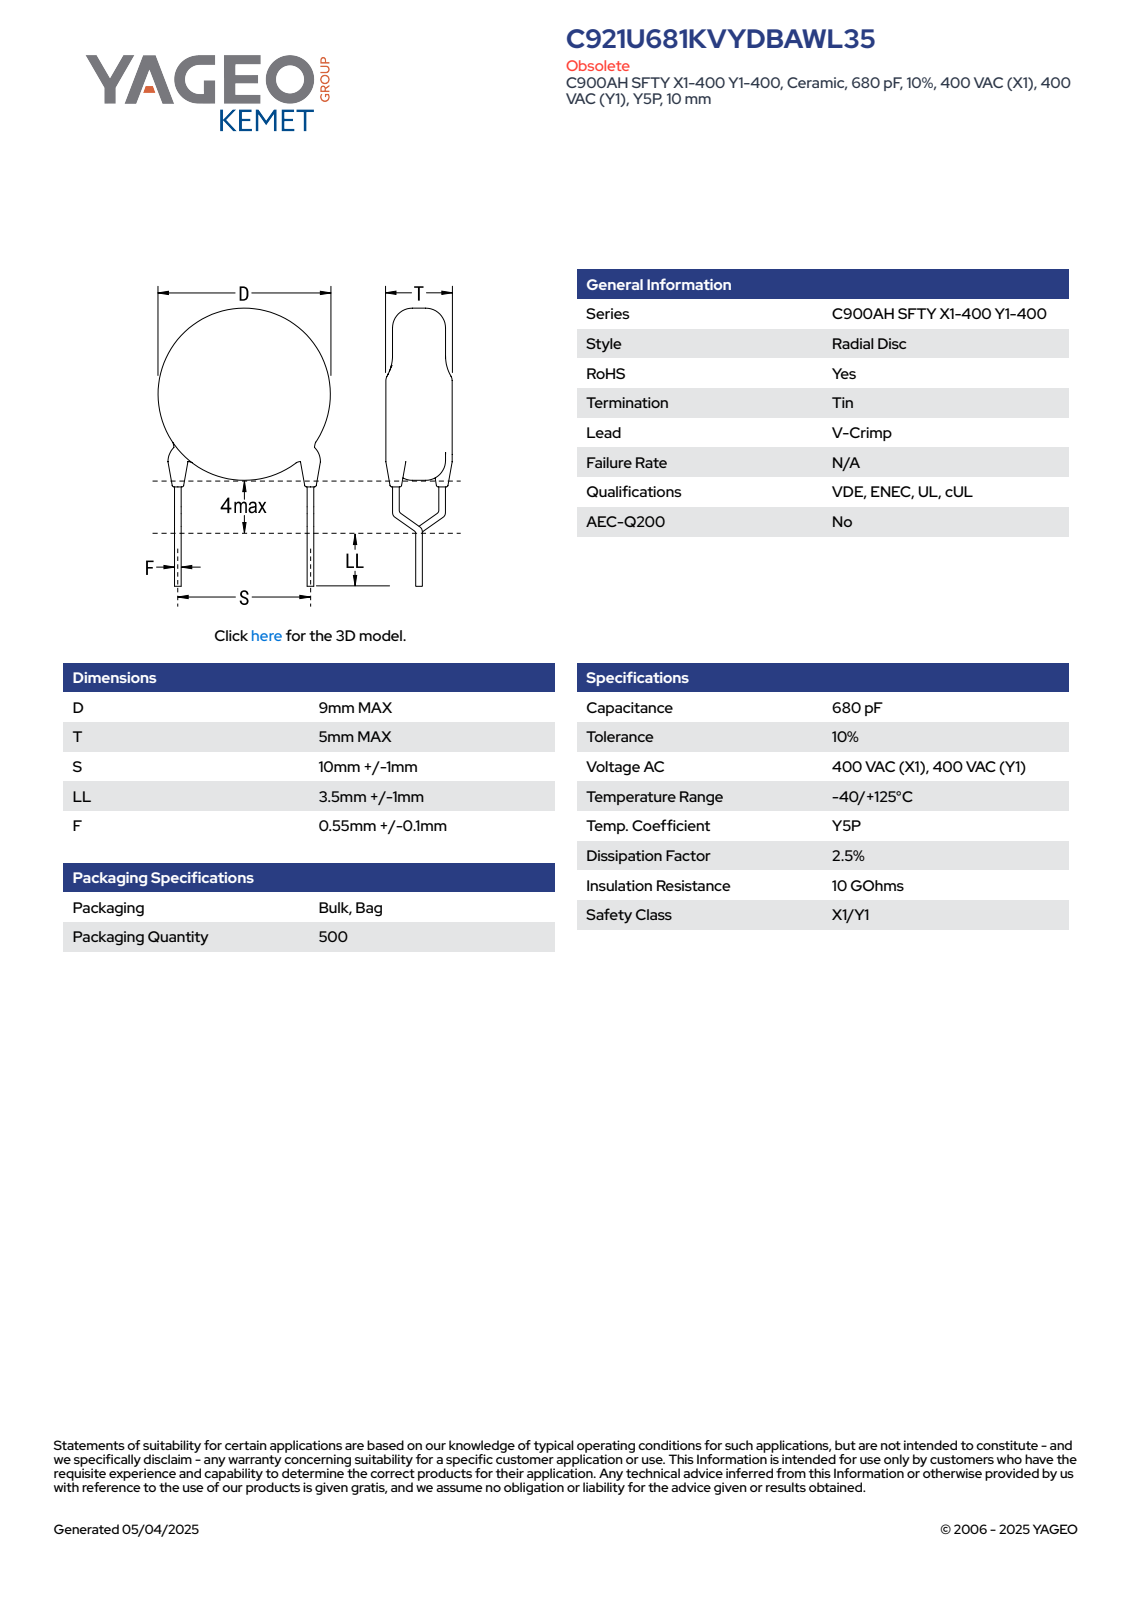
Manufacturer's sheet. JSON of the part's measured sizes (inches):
{"part_name": "CCD_VCC900_D9T5S10LL4.5F0.65", "step_written_by": "SolidWorks 2014 (AUTOMOTIVE_DESIGN)", "units": "inches", "bodies": {"solids": 5, "faces": 93, "planar": 65, "cylindrical": 16, "other": 12}, "overall_size": [0.681, 0.419, 0.197], "volume_in3": 0.019, "surface_area_in2": 0.468, "round_bosses_or_shafts": [[0.026, 6], [0.354, 1]], "face_to_face_distances": [0.197, 0.291, 0.046, 0.527, 0.235, 0.481, 0.189, 0.013, 0.188, 0.137]}
